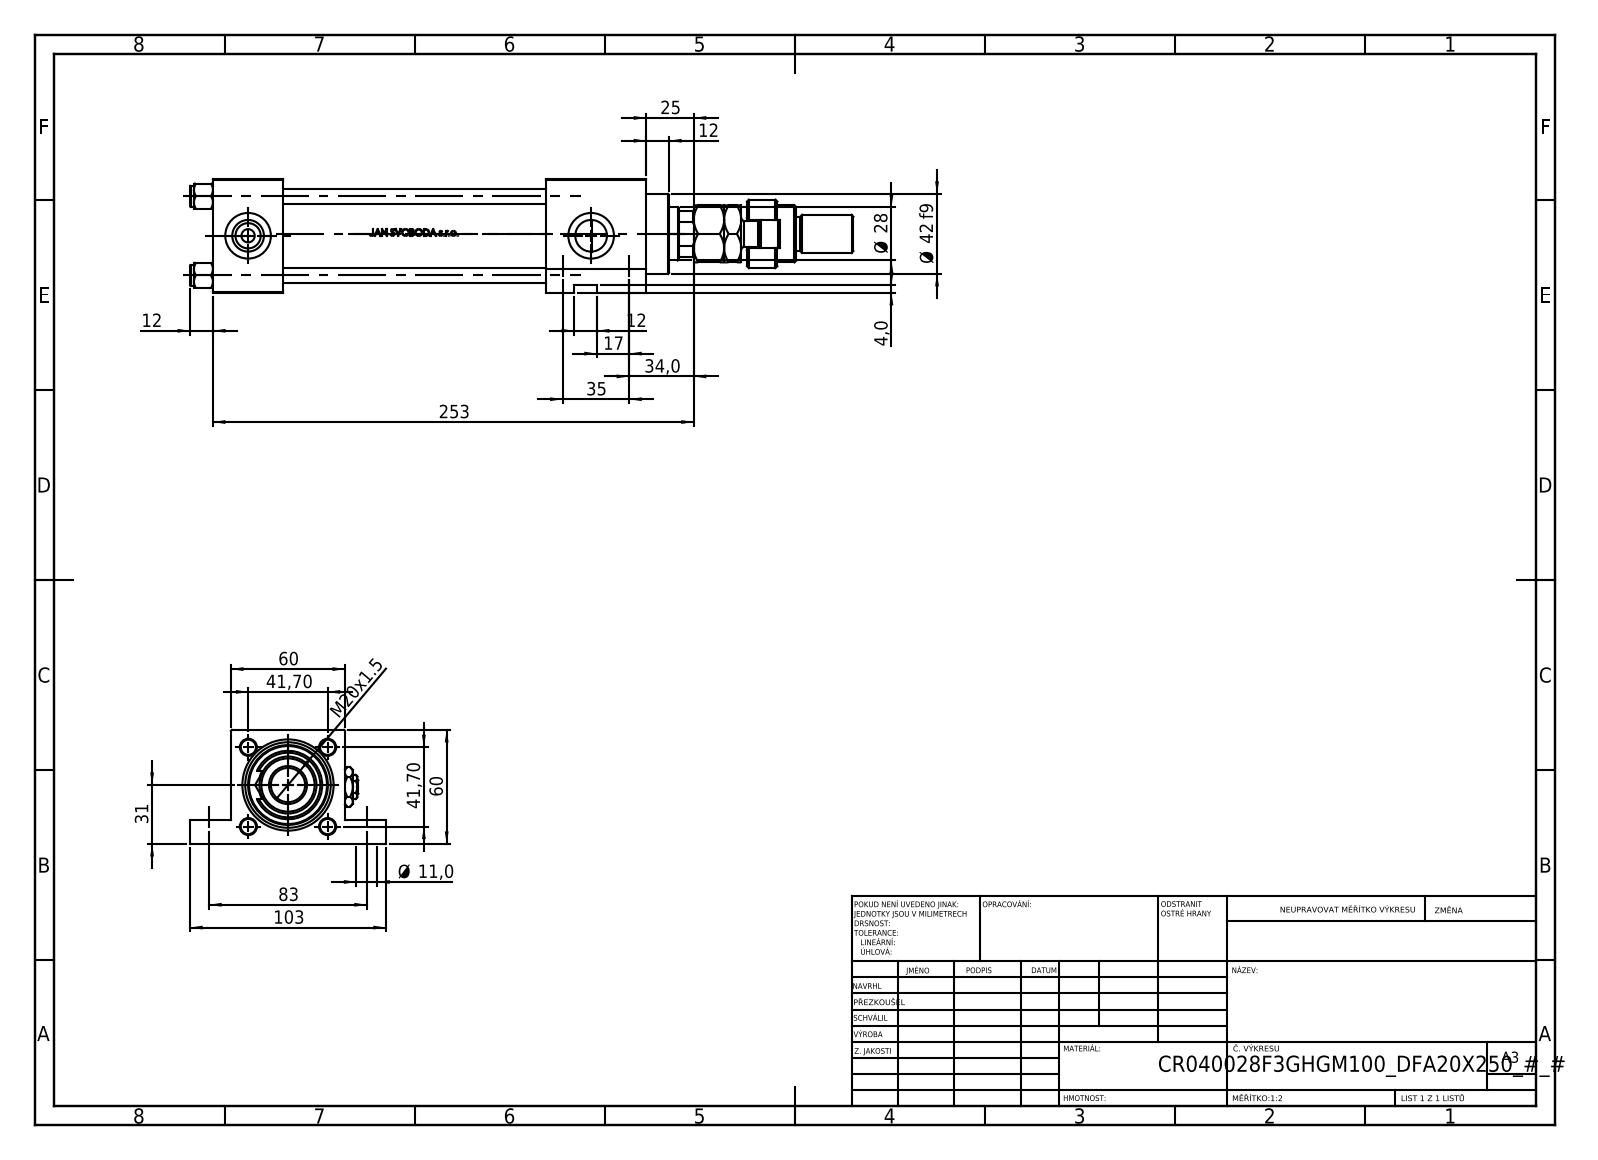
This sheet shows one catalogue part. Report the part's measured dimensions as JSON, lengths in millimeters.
{"part_name": "FEMALE_PART_FOR_DFA; V215CR_F_Body; MFA; Zatka_pro_OIL_PORT (+4 more)", "step_written_by": "SolidWorks 2019 (CONFIG_CONTROL_DESIGN)", "units": "millimeters", "bodies": {"solids": 15, "faces": 1300, "planar": 512, "cylindrical": 162, "other": 626}, "overall_size": [349, 103, 60], "volume_mm3": 588447, "surface_area_mm2": 170561, "round_holes": [[8, 4], [11, 4], [16.66, 3], [24, 3], [7, 2], [16, 1], [18.5, 1], [28, 1], [31, 1], [40, 1], [45, 1]], "round_bosses_or_shafts": [[11, 4], [46, 1], [42, 1], [36, 1], [30, 1], [22, 1], [20, 1], [18, 1]], "partial_cylinders_radius": [[7.5, 1], [12, 1], [13.5, 1]], "face_to_face_distances": [60, 37, 53, 175, 138, 228, 38, 191, 12.5, 47.5], "hole_center_spacings": [41.7, 28.79, 30.2, 35, 58.97, 83, 90.08, 8]}
